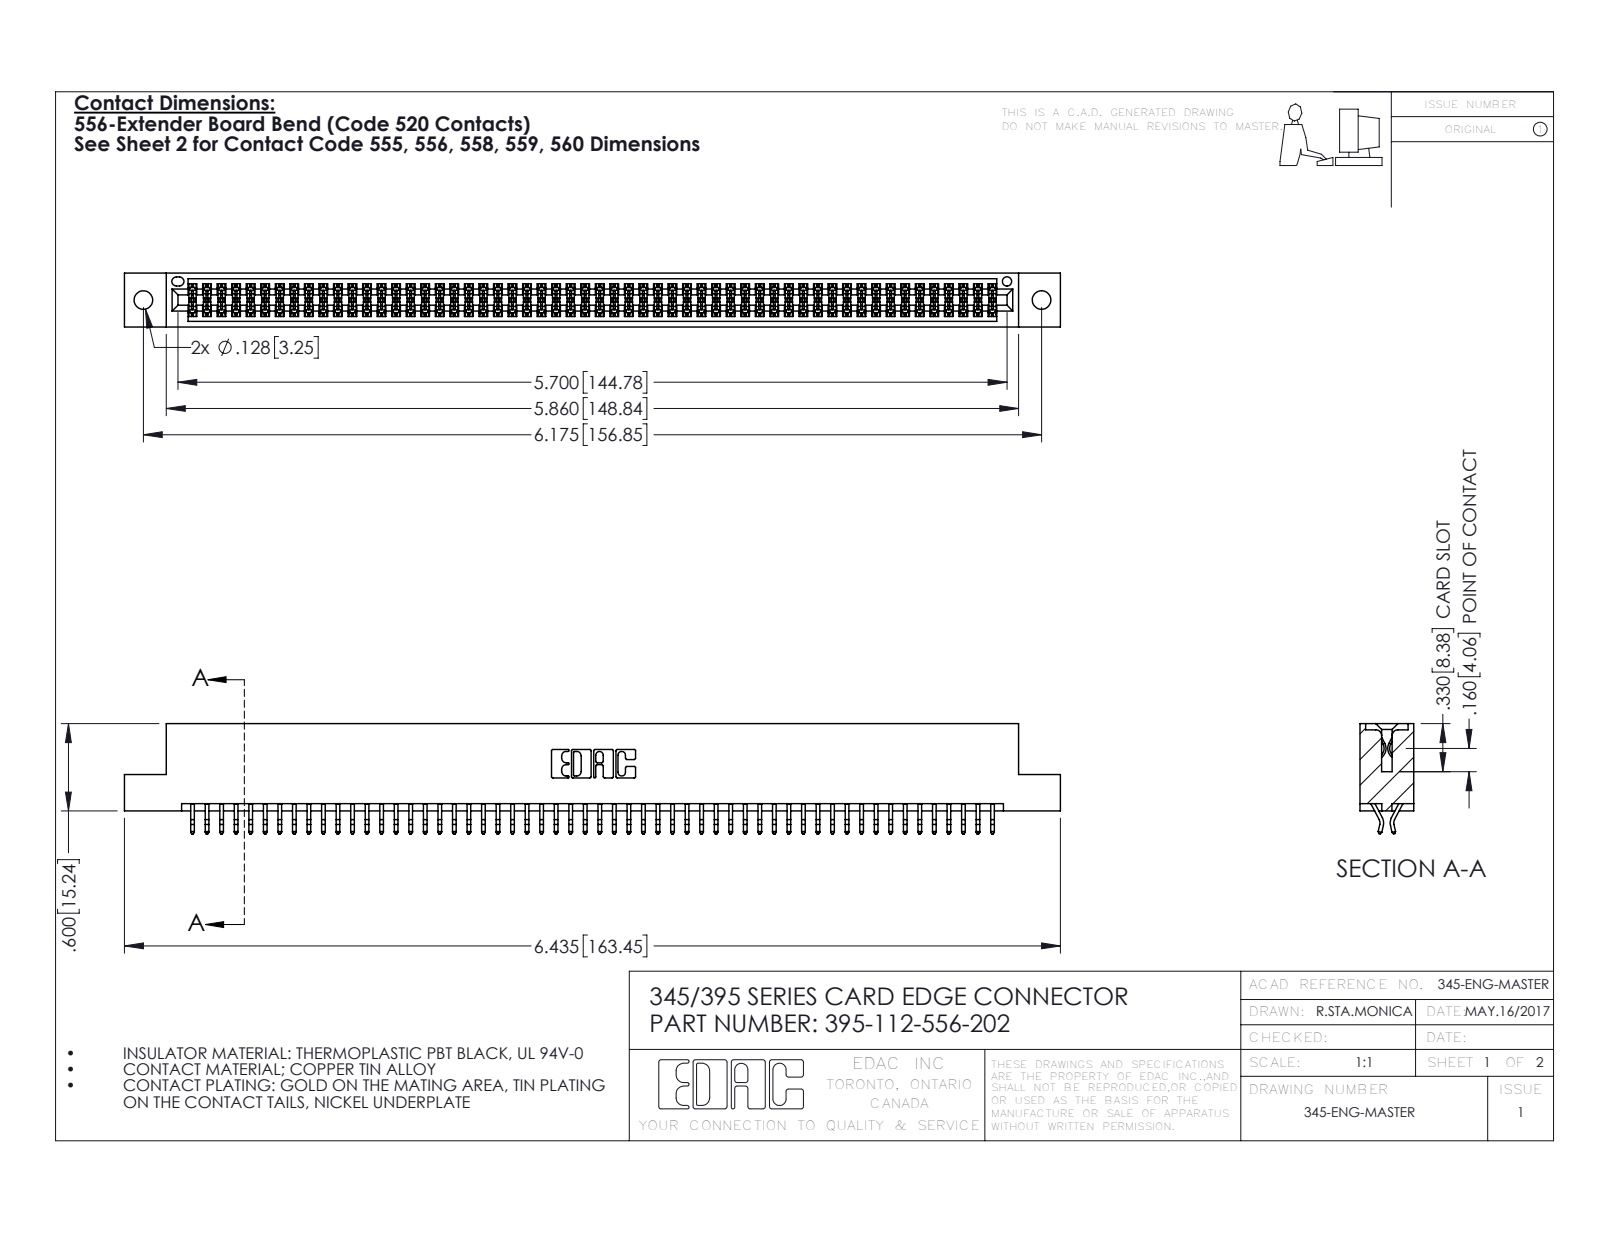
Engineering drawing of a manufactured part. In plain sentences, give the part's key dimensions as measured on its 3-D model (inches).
The part is named "345-292-001_556 Tail; 395-112-556-202; 345 Part_Flush Mounting Lugs - 0.128 Dia". Its 3-D file was written by "SolidWorks 2016 (CONFIG_CONTROL_DESIGN)". It is 113 solids with 6398 faces: 4224 planar, 2174 cylindrical and 0 other. Overall it measures 6.435 by 0.757 by 0.37 inches. Its volume is 0.974 cubic inches and its surface area 36.43 square inches. Round holes: 2 of diameter 0.128, 1 of diameter 0.064. Partial cylindrical surfaces (rounded edges, fillets, slot ends): 168 of radius 0.006, 22 of radius 0.01, 6 of radius 0.007, 6 of radius 0.031, 3 of radius 0.026, 2 of radius 0.01, 2 of radius 0.014, 2 of radius 0.019. The main face-to-face distances are 0.298, 0.072, 0.37, 0.2, 0.025, 0.098, 0.272, 0.225, 0.175, 0.149. The hole center spacings are 0.27, 5.939, 6.175.
